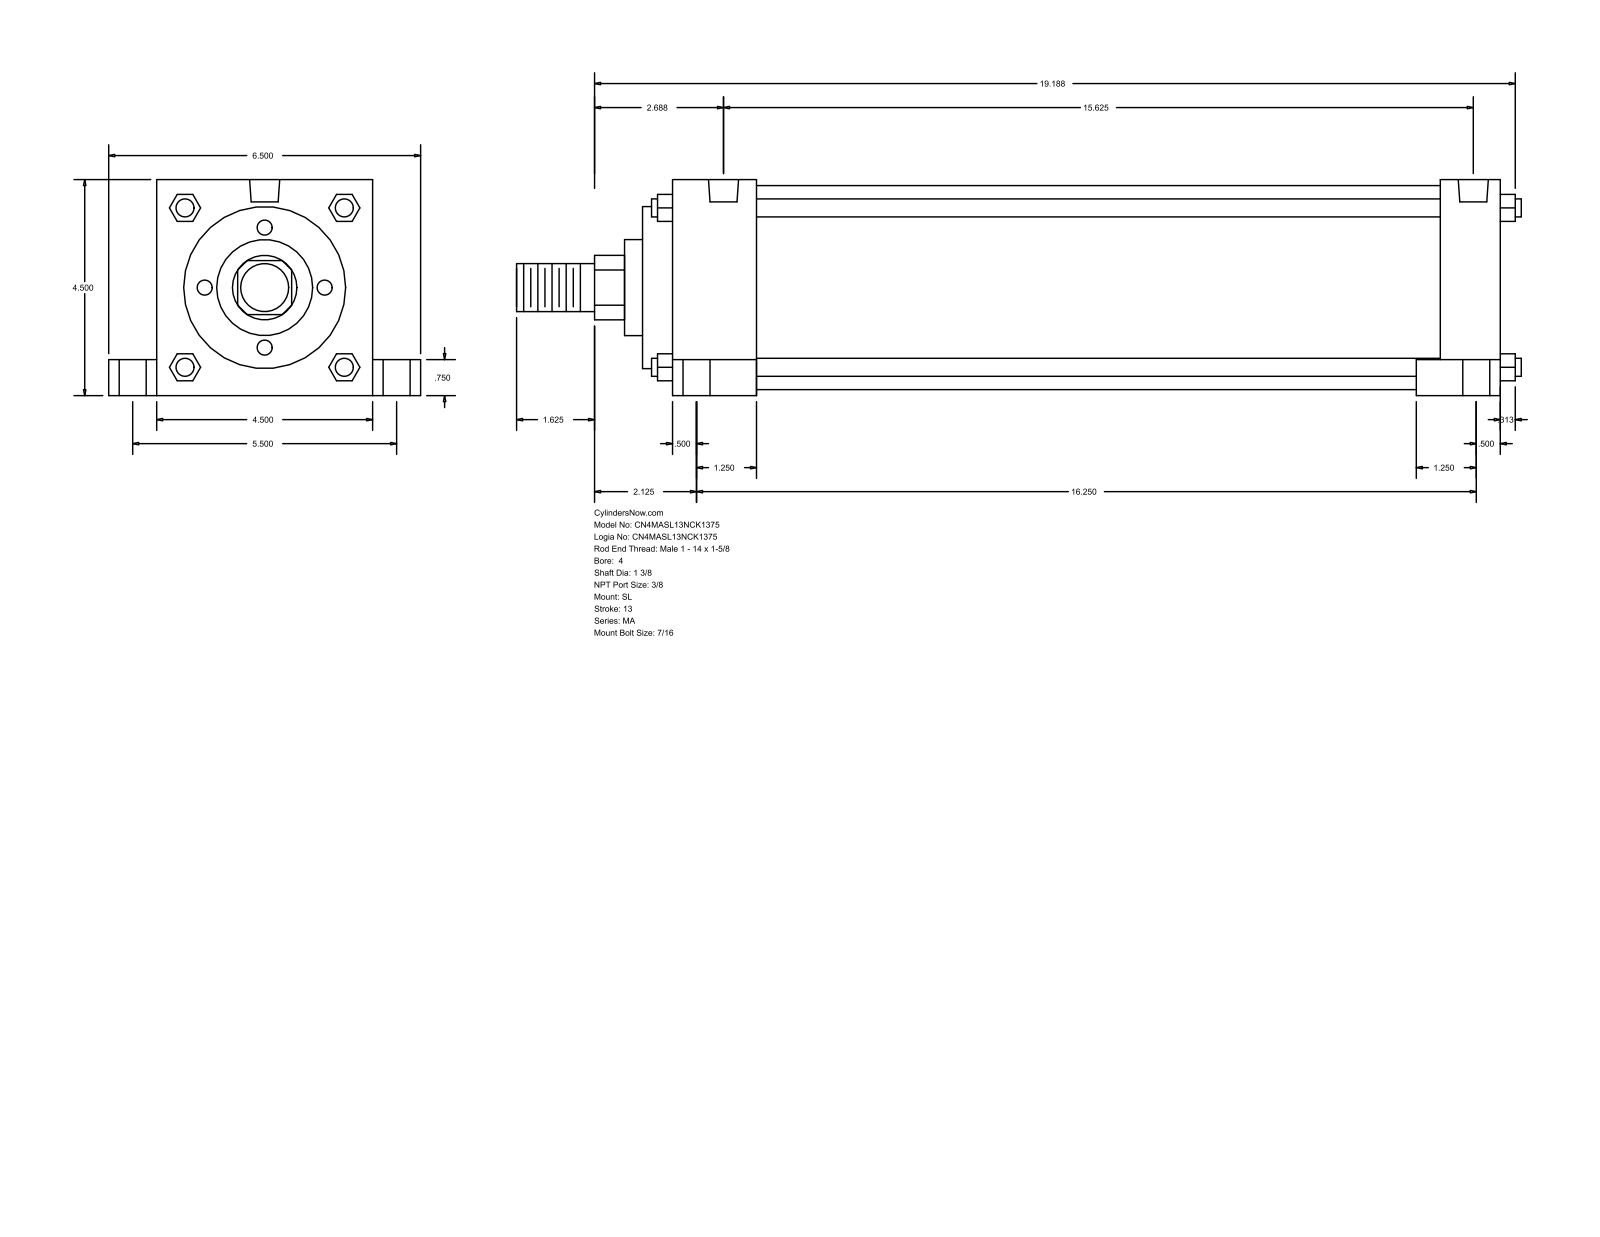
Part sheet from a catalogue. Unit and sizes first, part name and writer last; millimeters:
Units: millimetres
Overall size (bounding box): 531.81 × 165.1 × 114.3
Round holes (diameter × count): ⌀11.11 ×4, ⌀14.29 ×4, ⌀20.64 ×4, ⌀15.93 ×2
Round bosses / shafts (diameter × count): ⌀9.53 ×4, ⌀107.95 ×1, ⌀85.72 ×1, ⌀50.8 ×1, ⌀34.92 ×1, ⌀25.4 ×1
Partial cylindrical surfaces — rounded edges, fillets, slot ends (radius × count): R17.06 ×1
Main face-to-face distances: 114.3, 438.16, 15.87, 454.03, 60.32, 44.45, 393.71, 422.28, 406.41, 361.96
Hole centre spacings: 69.87, 70.14, 71.29, 72.4, 139.7, 387.35, 399.85, 404.55
Bodies: 0 solids, 150 faces (113 planar, 37 cylindrical, 0 other)
Part name (STEP PRODUCT): MA_SL__0400_1.375
STEP written by: GSSL Pune (CONFIG_CONTROL_DESIGN)
